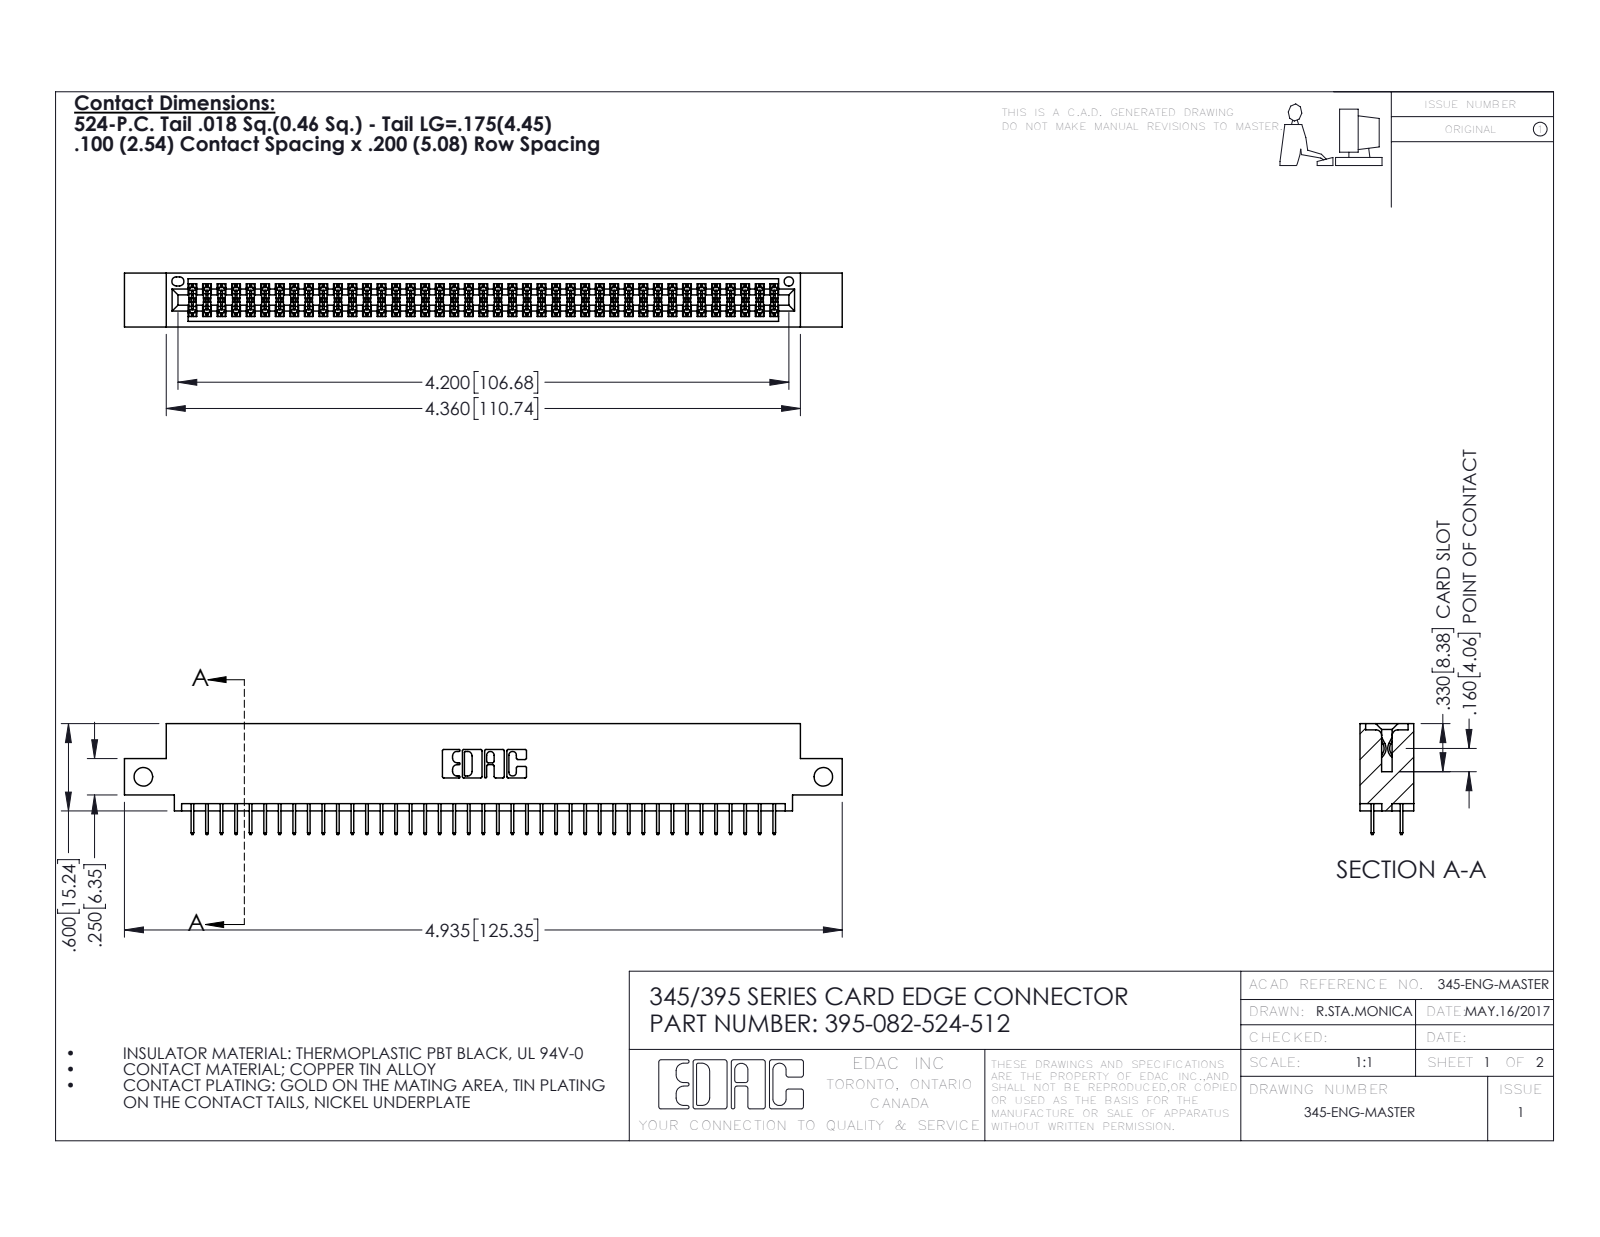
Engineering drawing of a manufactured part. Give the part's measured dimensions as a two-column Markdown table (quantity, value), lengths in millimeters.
| quantity | value |
| --- | --- |
| part name | 395-082-524-512; 345-292-001_345-293-124; 345 Part_0.110 Offset - Side Mount |
| STEP written by | SolidWorks 2016 (CONFIG_CONTROL_DESIGN) |
| units | millimeters |
| bodies | 83 solids, 4558 faces (3282 planar, 1276 cylindrical, 0 other) |
| overall size | 125.3 × 19.4 × 9.4 |
| volume | 11 900 mm³ |
| surface area | 17 170 mm² |
| round holes (diameter × count) | 3.3 × 2, 1.6 × 1 |
| partial cylindrical surfaces (radius × count) | 0.2 × 123, 0.3 × 22, 0.2 × 6, 0.8 × 6, 0.7 × 3, 0.4 × 2, 0.5 × 2, 0.6 × 2 |
| main face-to-face distances | 1.8, 7.6, 9.4, 5.1, 2.5, 6.9, 0.6, 5.7, 1.8, 4.4 |
| hole center spacings | 118.7 |
